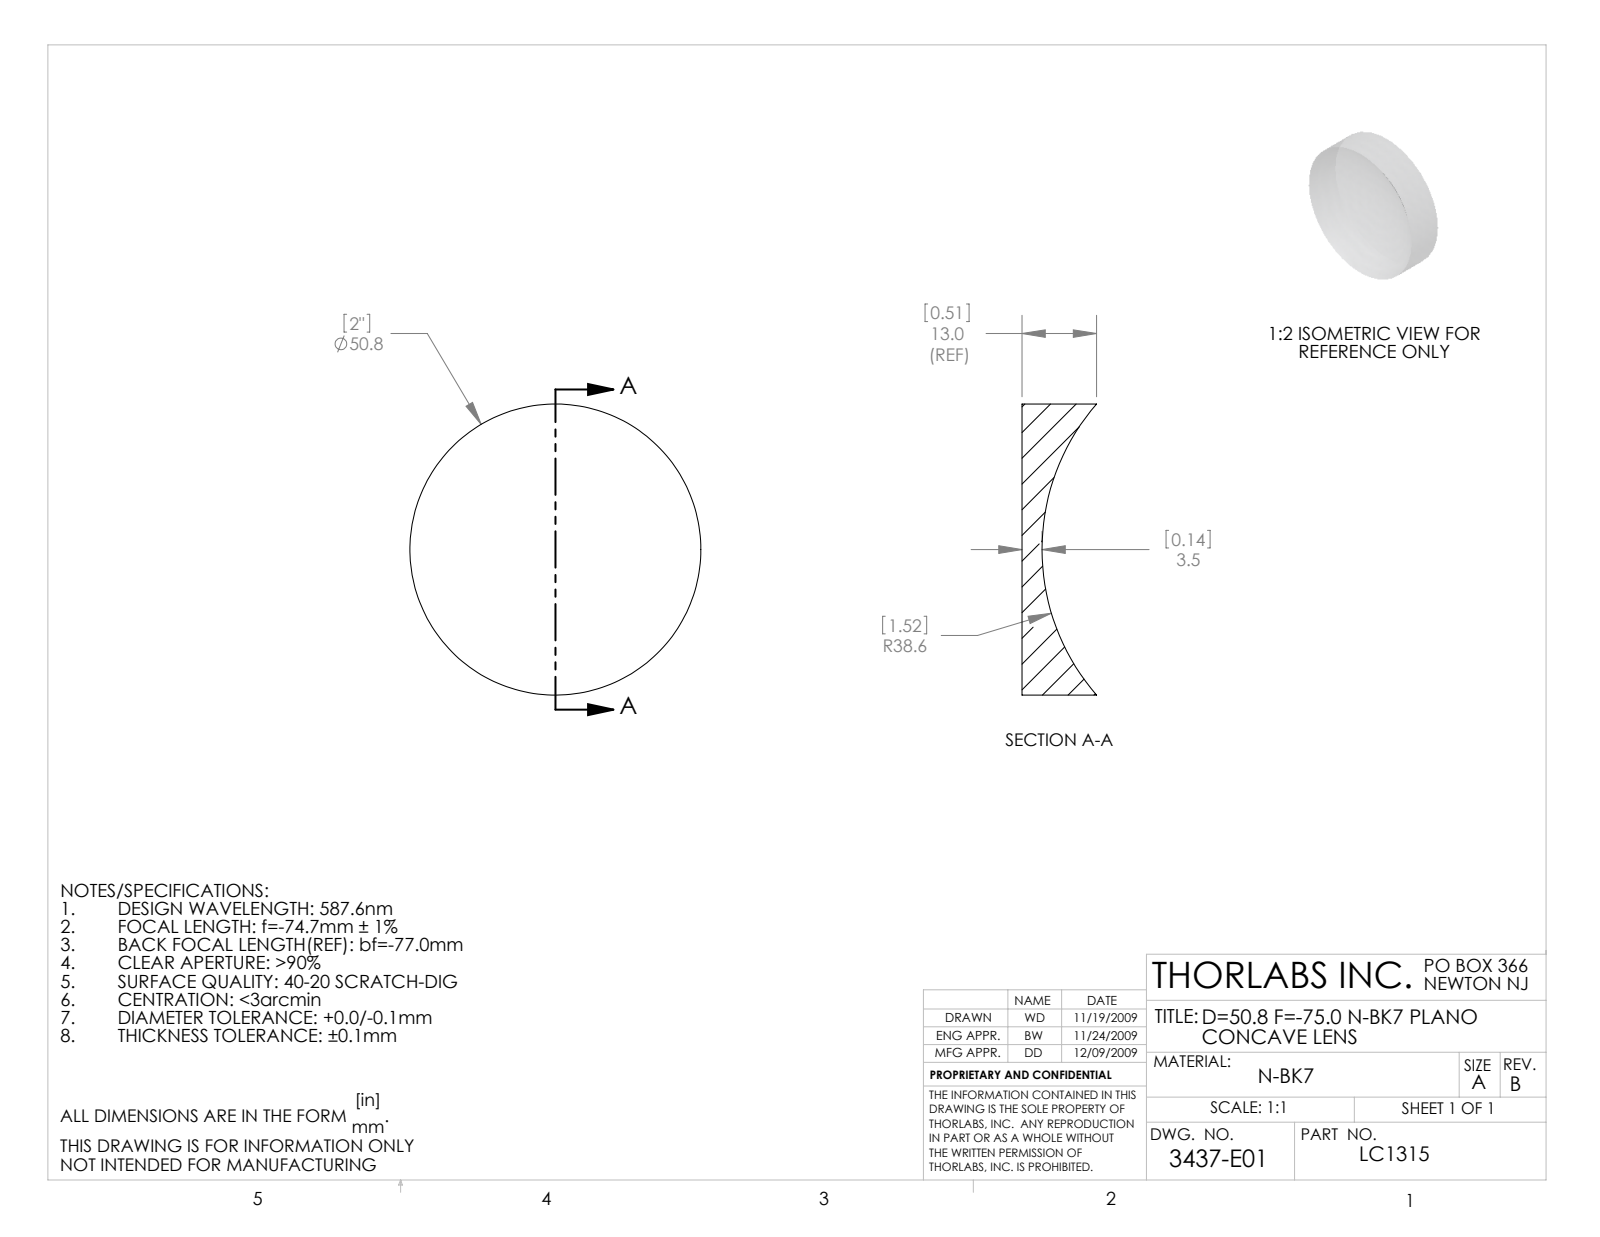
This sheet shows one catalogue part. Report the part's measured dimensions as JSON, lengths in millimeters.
{"part_name": "3437-E0W", "step_written_by": "SolidWorks 2009 (AUTOMOTIVE_DESIGN)", "units": "millimeters", "bodies": {"solids": 1, "faces": 5, "planar": 1, "cylindrical": 2, "other": 2}, "overall_size": [50.8, 50.8, 13.04], "volume_mm3": 16305, "surface_area_mm2": 6420, "round_bosses_or_shafts": [[50.8, 1]]}
